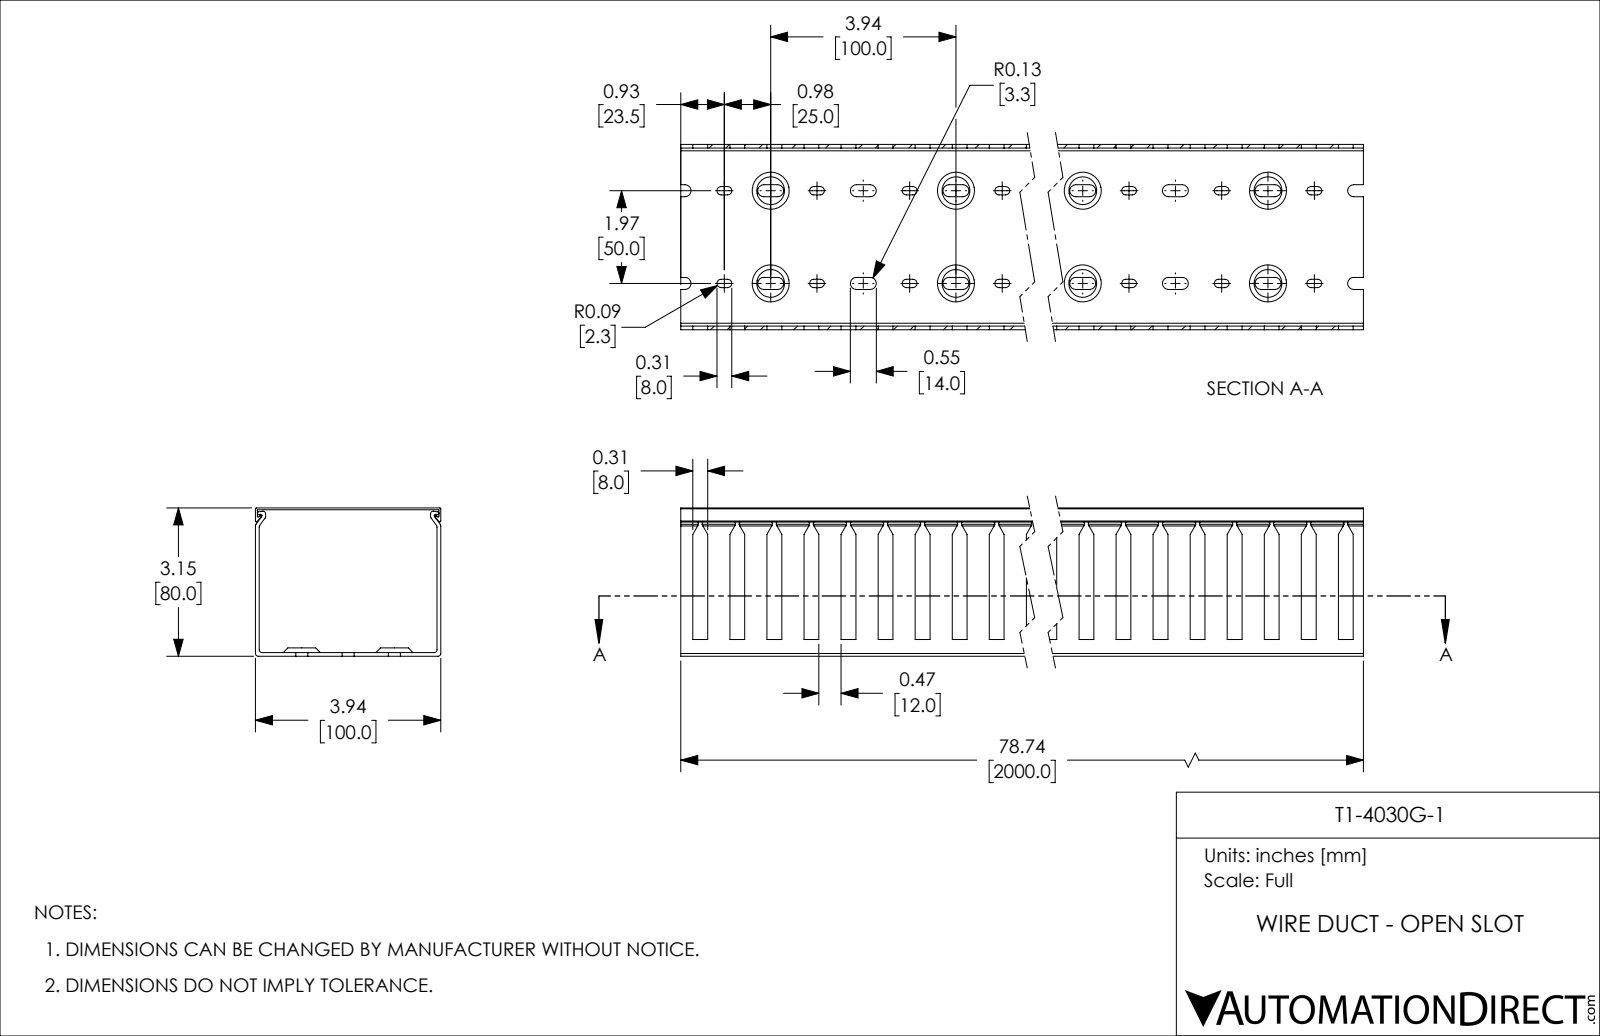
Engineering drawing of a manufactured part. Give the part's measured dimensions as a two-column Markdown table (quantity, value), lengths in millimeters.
| quantity | value |
| --- | --- |
| part name | T1-4030G-1 |
| STEP written by | SolidWorks 2021 (CONFIG_CONTROL_DESIGN) |
| units | millimeters |
| bodies | 2 solids, 1573 faces (762 planar, 731 cylindrical, 80 other) |
| overall size | 2000 × 100 × 80 |
| volume | 1 244 000 mm³ |
| surface area | 1 484 000 mm² |
| partial cylindrical surfaces (radius × count) | 3.25 × 200, 2.25 × 160, 1.5 × 12, 0.5 × 8, 0.75 × 6 |
| main face-to-face distances | 2, 98, 1, 80, 79, 77, 78, 100, 96, 99 |
